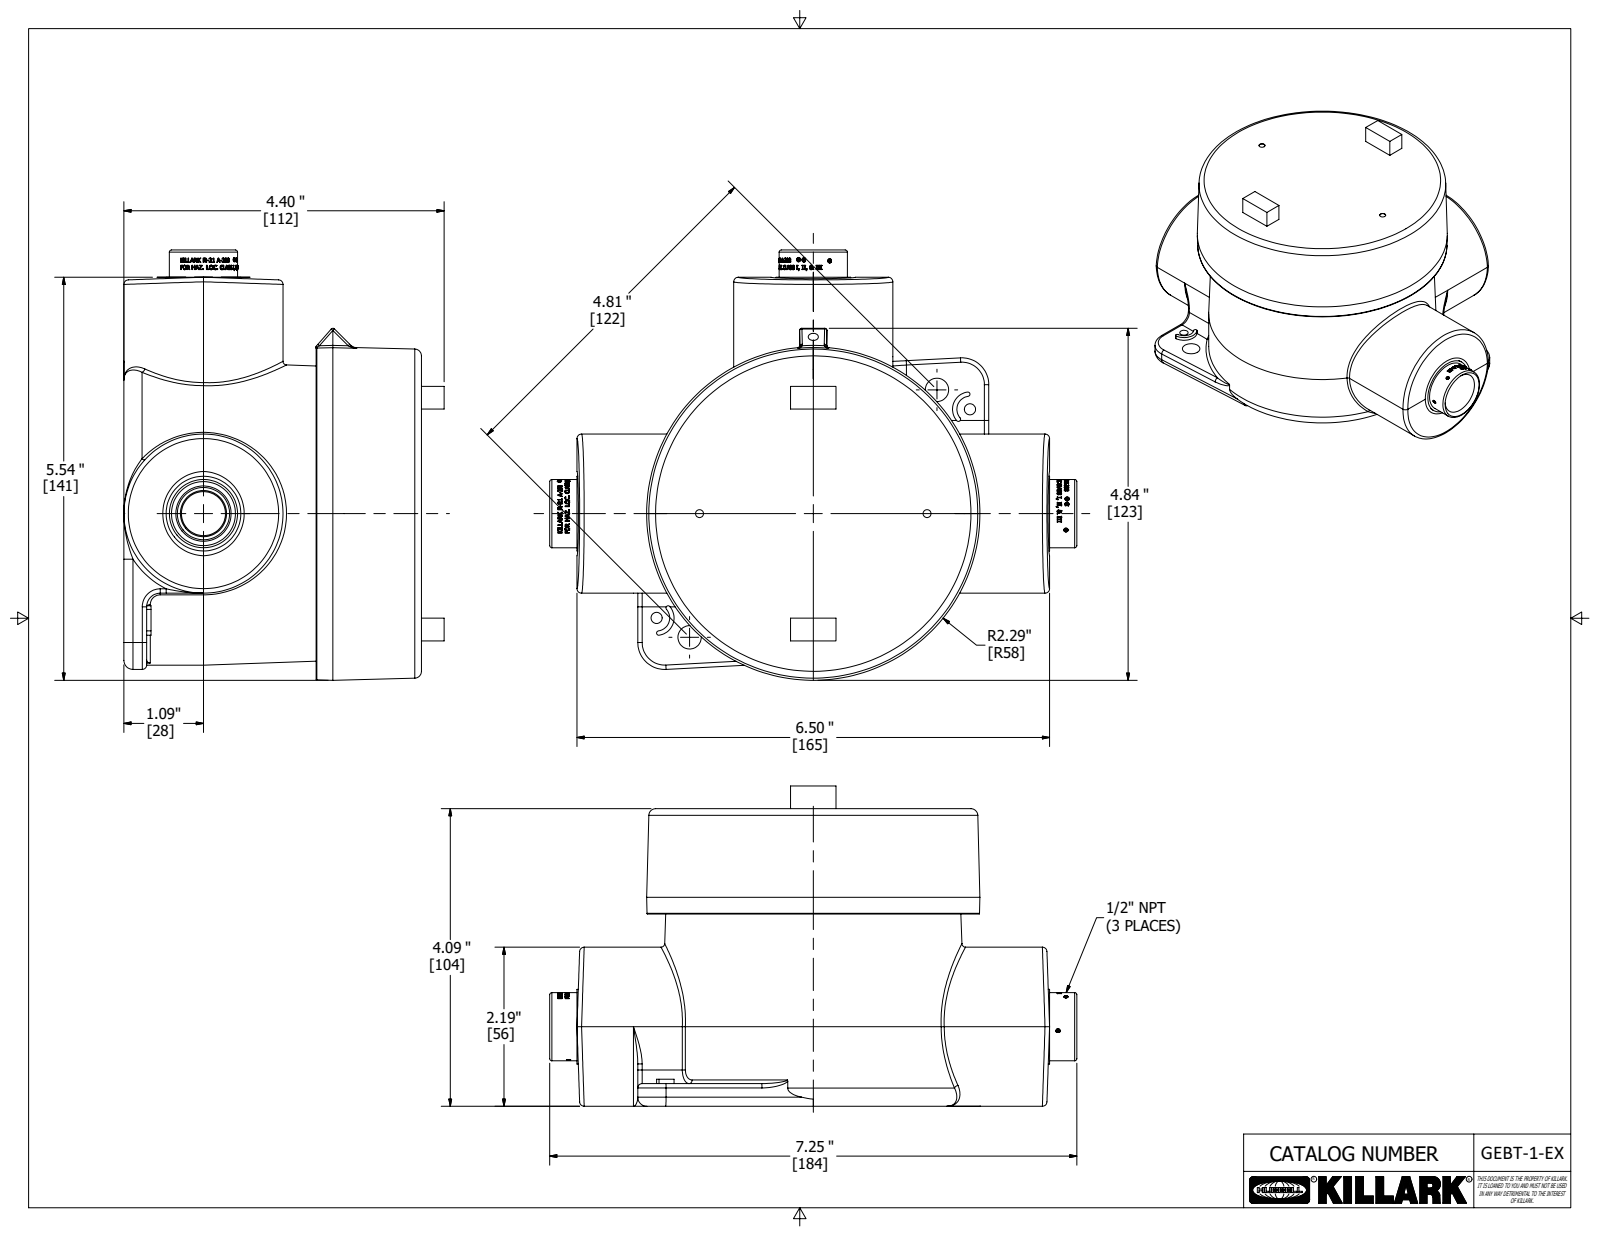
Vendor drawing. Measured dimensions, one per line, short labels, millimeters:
name: GEBT-1-EX; 21155; 23649AAAM; 00398
written by: Autodesk Inventor 2020 (AUTOMOTIVE_DESIGN)
unit: mm
bodies: 5 solids, 2909 faces (1318 planar, 314 cylindrical, 1277 other)
size: 231.1 × 150.3 × 111.9
volume: 683 000 mm³; area: 147 900 mm²
holes: 2× ⌀2.8, 2× ⌀3.9, 2× ⌀8.2, 2× ⌀20.1, 2× ⌀39.6, 1× ⌀3.5, 1× ⌀97.1, 1× ⌀102.7
bosses: 2× ⌀55.6, 2× ⌀23.8
rounds: 35× R1.5, 14× R0.8, 4× R3.2, 3× R0.8, 3× R4.7, 2× R4.6, 2× R6.1, 2× R9.4
face distances: 104, 92.8, 11.1, 88.9, 3.9, 15.1, 36.8, 67.2, 21.7, 25.7
hole spacings: 13.4, 39.4, 39.8, 43.4, 61.1, 65.8, 93.5, 101.3
